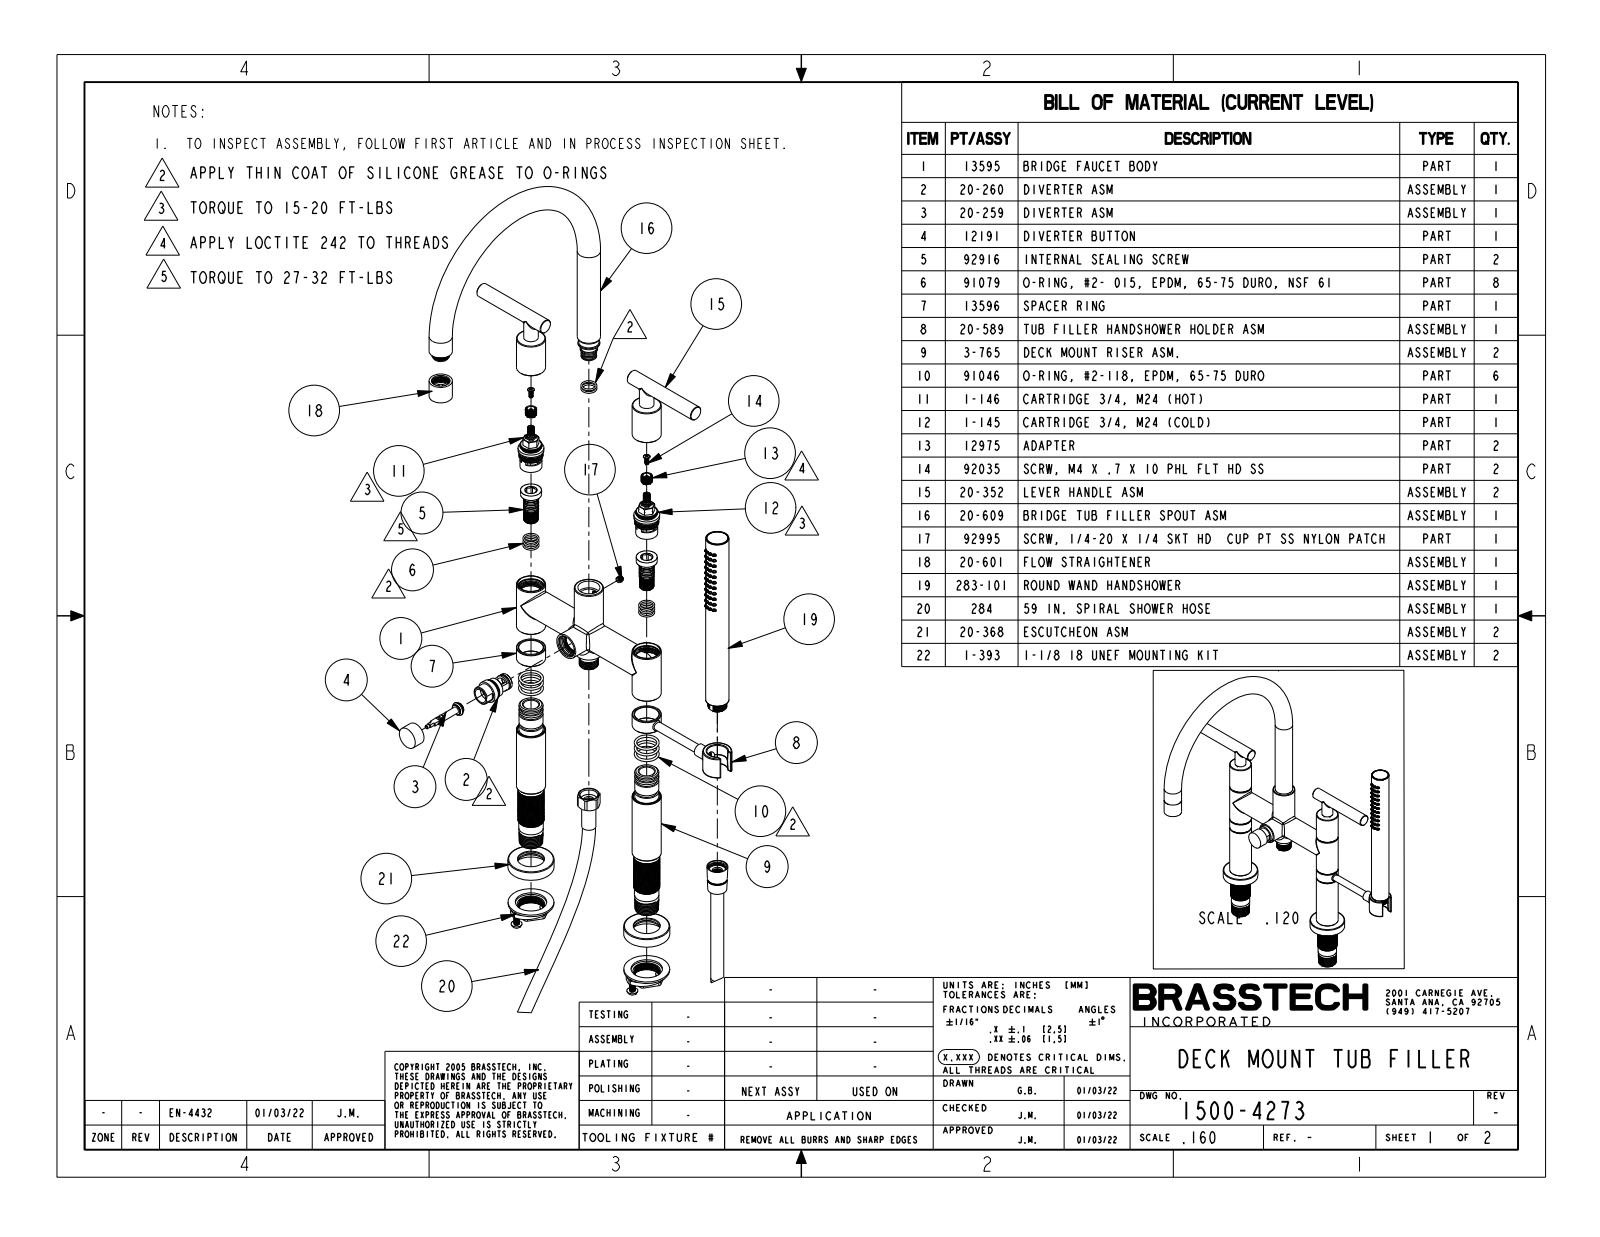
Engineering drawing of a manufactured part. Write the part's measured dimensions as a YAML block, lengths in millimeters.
part_name: "1500-4273"
step_written_by: "CREO PARAMETRIC BY PTC INC, 2019352 (CONFIG_CONTROL_DESIGN)"
units: millimeters
bodies: {solids: 5, faces: 1172, planar: 123, cylindrical: 307, other: 742}
overall_size: [858.3, 389.4, 266.4]
volume: 1185000
surface_area: 215900
round_holes:
  - {diameter: 3.6, count: 44}
  - {diameter: 5.2, count: 1}
  - {diameter: 17.6, count: 1}
round_bosses_or_shafts:
  - {diameter: 31.8, count: 5}
  - {diameter: 25.4, count: 3}
  - {diameter: 15.9, count: 3}
  - {diameter: 14.2, count: 3}
  - {diameter: 50.3, count: 2}
  - {diameter: 29.2, count: 2}
  - {diameter: 24.5, count: 1}
  - {diameter: 21, count: 1}
partial_cylinders:
  - {radius: 0.8, count: 6}
  - {radius: 10.4, count: 1}
  - {radius: 12.5, count: 1}
  - {radius: 14.2, count: 1}
face_to_face_distances: [10.8, 199.1, 188.3, 199.1, 188.3, 91.8, 199.3, 188.5, 107.6, 323.5]
hole_center_spacings: [8.5, 15.3, 4.3, 22.5, 29.8, 7.4, 11.4, 14.7]
